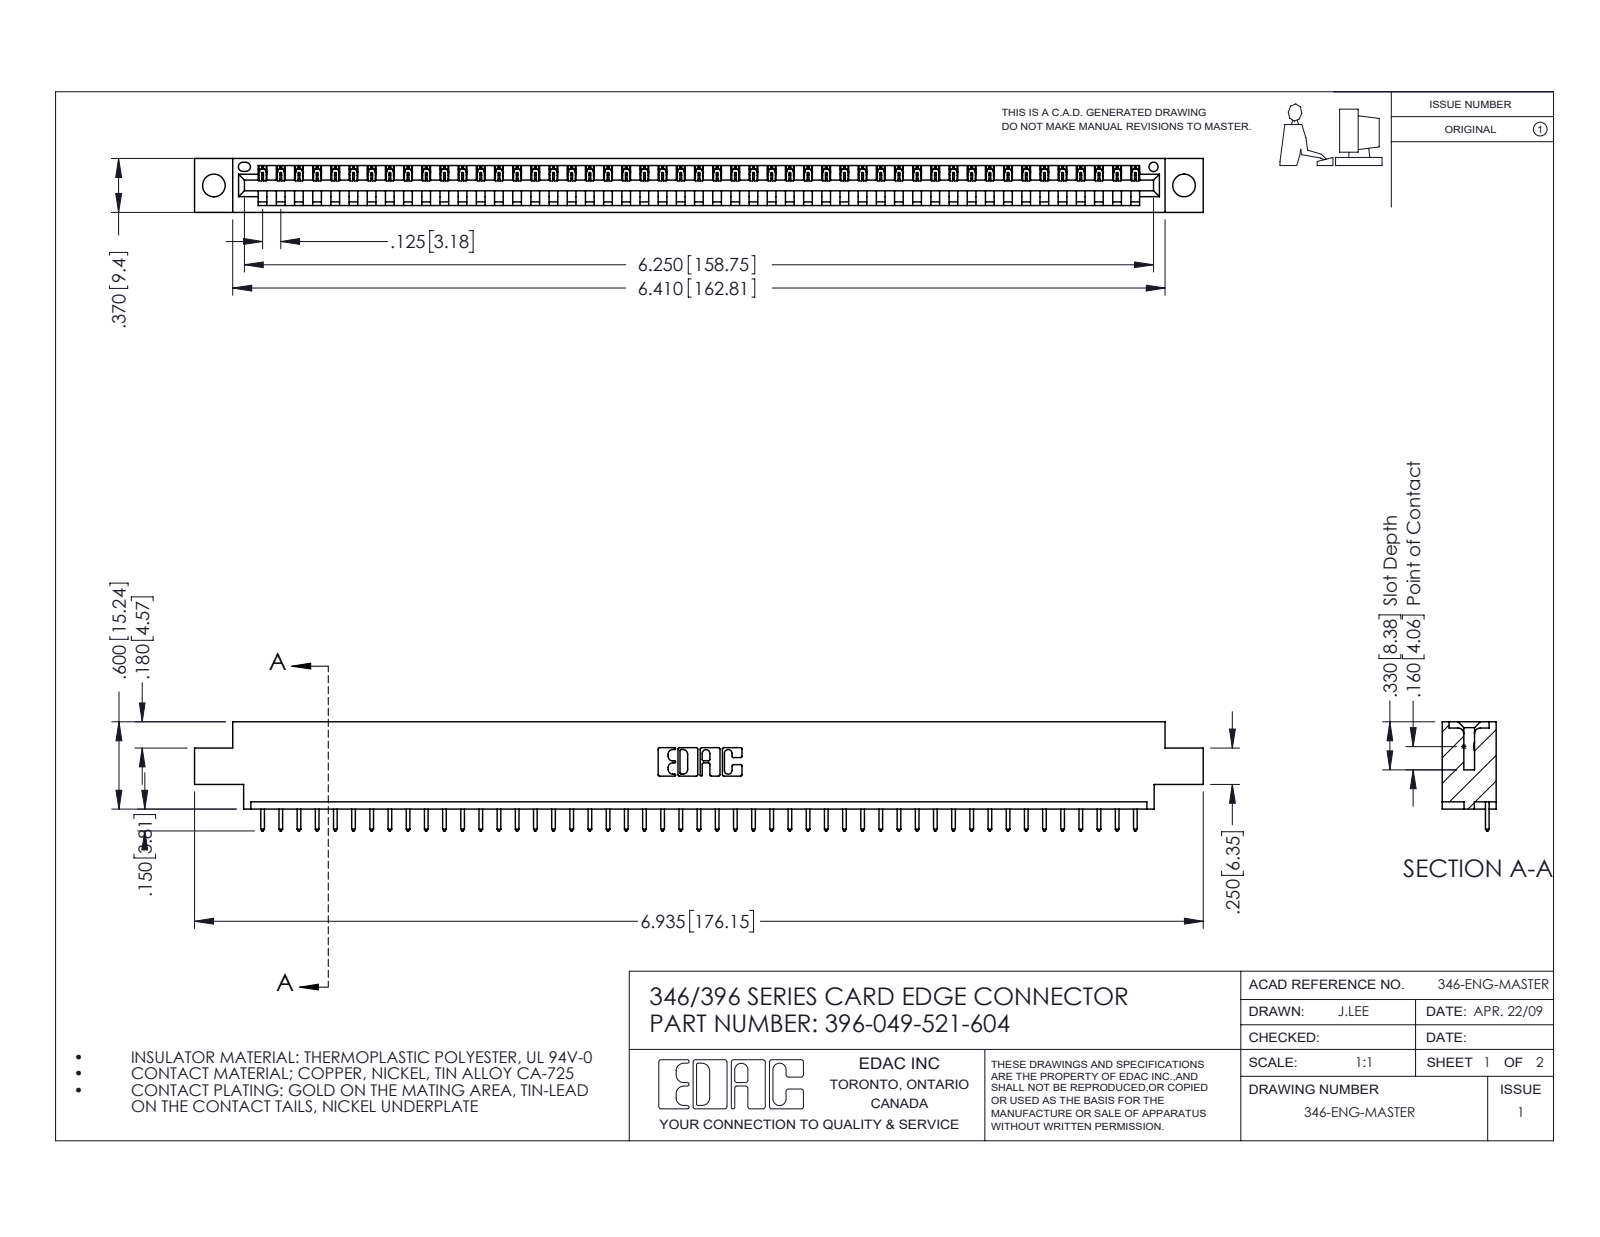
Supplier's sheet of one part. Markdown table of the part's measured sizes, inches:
| quantity | value |
| --- | --- |
| part name | 346 Part_0.170 Offset - 0.156 Dia-TH; 396-049-521-604; 345-292-001_345-293-121 |
| STEP written by | SolidWorks 2016 (CONFIG_CONTROL_DESIGN) |
| units | inches |
| bodies | 50 solids, 2968 faces (2040 planar, 928 cylindrical, 0 other) |
| overall size | 6.935 × 0.75 × 0.37 |
| volume | 1.009 in³ |
| surface area | 31.22 in² |
| round holes (diameter × count) | 0.156 × 2, 0.064 × 1 |
| partial cylindrical surfaces (radius × count) | 0.006 × 98, 0.01 × 98, 0.01 × 22, 0.007 × 6, 0.031 × 6, 0.026 × 3, 0.031 × 2, 0.04 × 2 |
| main face-to-face distances | 0.048, 0.322, 0.37, 0.25, 0.072, 0.298, 0.025, 0.148, 0.222, 0.1 |
| hole center spacings | 0.246, 6.461, 6.67 |
